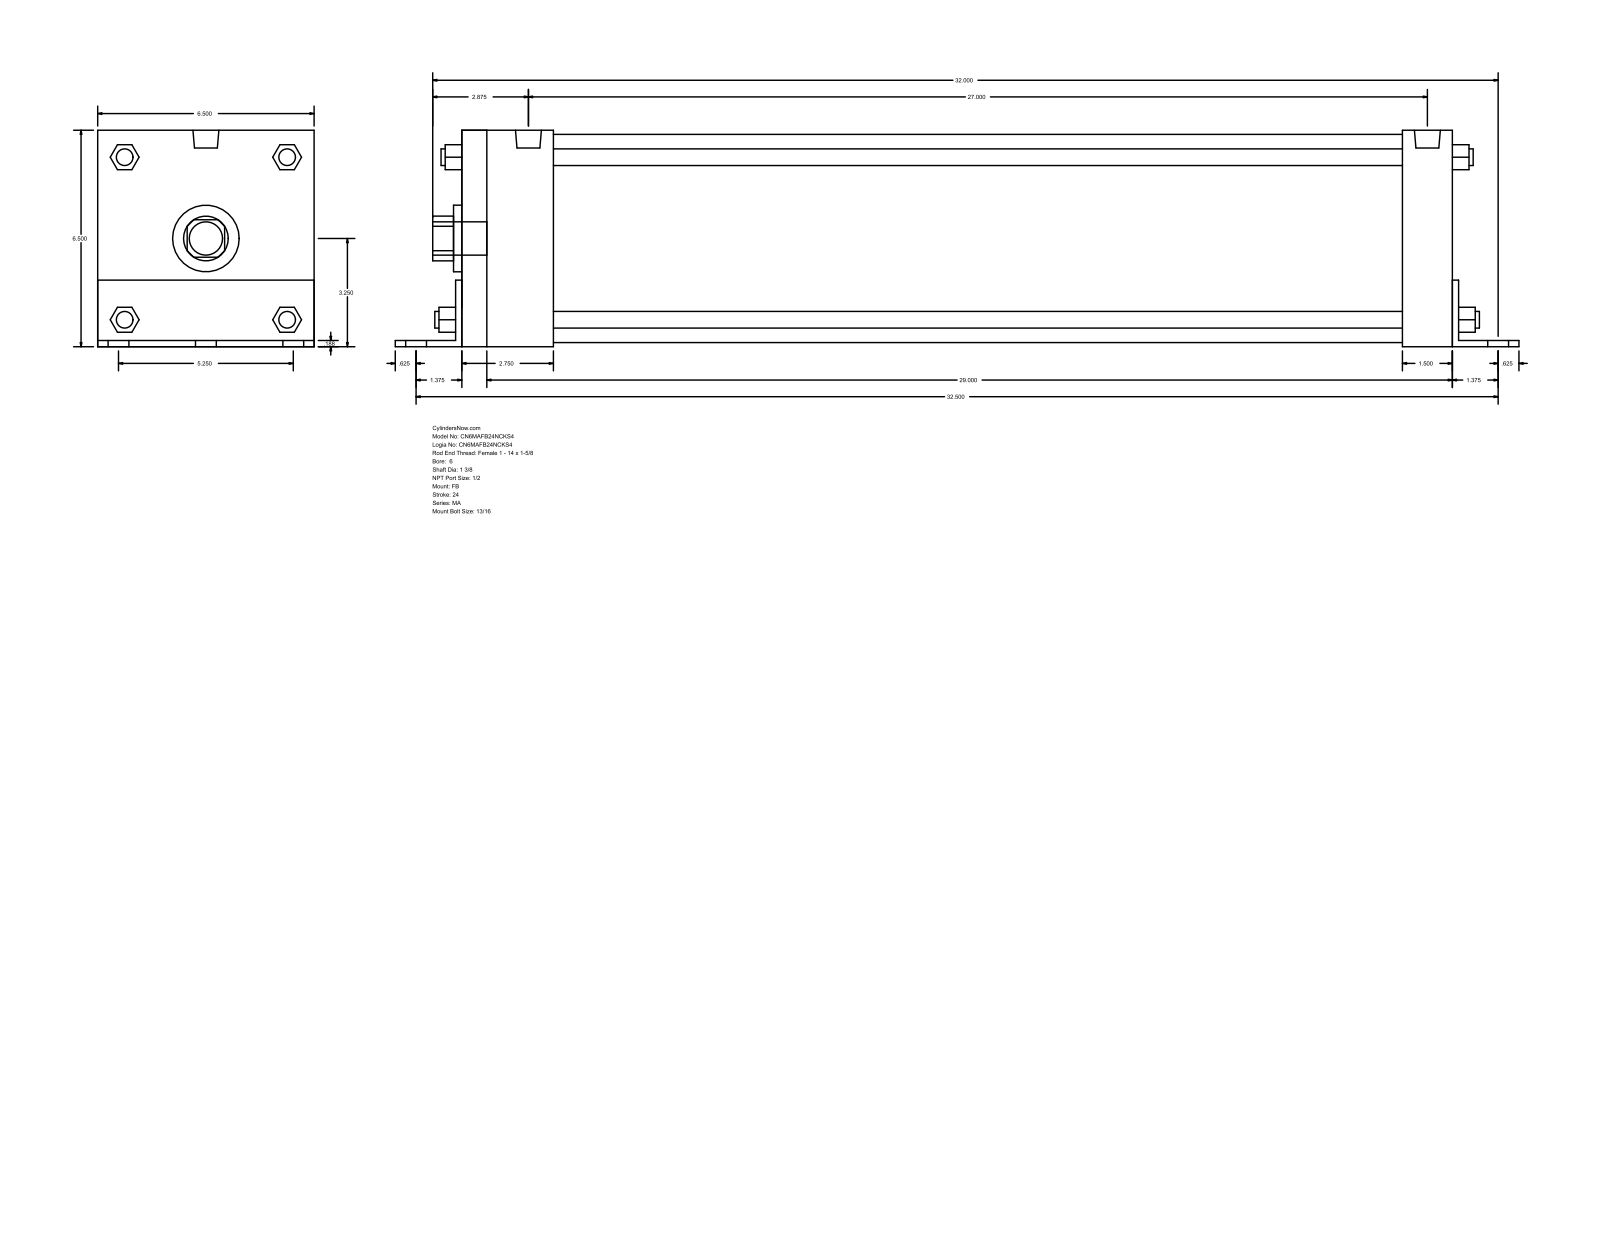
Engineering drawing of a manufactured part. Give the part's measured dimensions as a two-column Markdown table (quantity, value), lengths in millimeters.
| quantity | value |
| --- | --- |
| part name | MA_FB__0600_1.375 |
| STEP written by | GSSL Pune (CONFIG_CONTROL_DESIGN) |
| units | millimeters |
| bodies | 0 solids, 140 faces (105 planar, 35 cylindrical, 0 other) |
| overall size | 854.08 × 165.15 × 165.1 |
| round holes (diameter × count) | 34.92 × 1, 50.8 × 1, 158.75 × 1 |
| round bosses / shafts (diameter × count) | 20.64 × 6, 17.46 × 4, 12.7 × 4, 19.77 × 2, 25.4 × 1 |
| partial cylindrical surfaces (radius × count) | 17.06 × 1, 32.05 × 1 |
| main face-to-face distances | 165.1, 4.76, 752.47, 165.15, 4.71, 160.39, 4.77, 38.1, 757.24, 762 |
